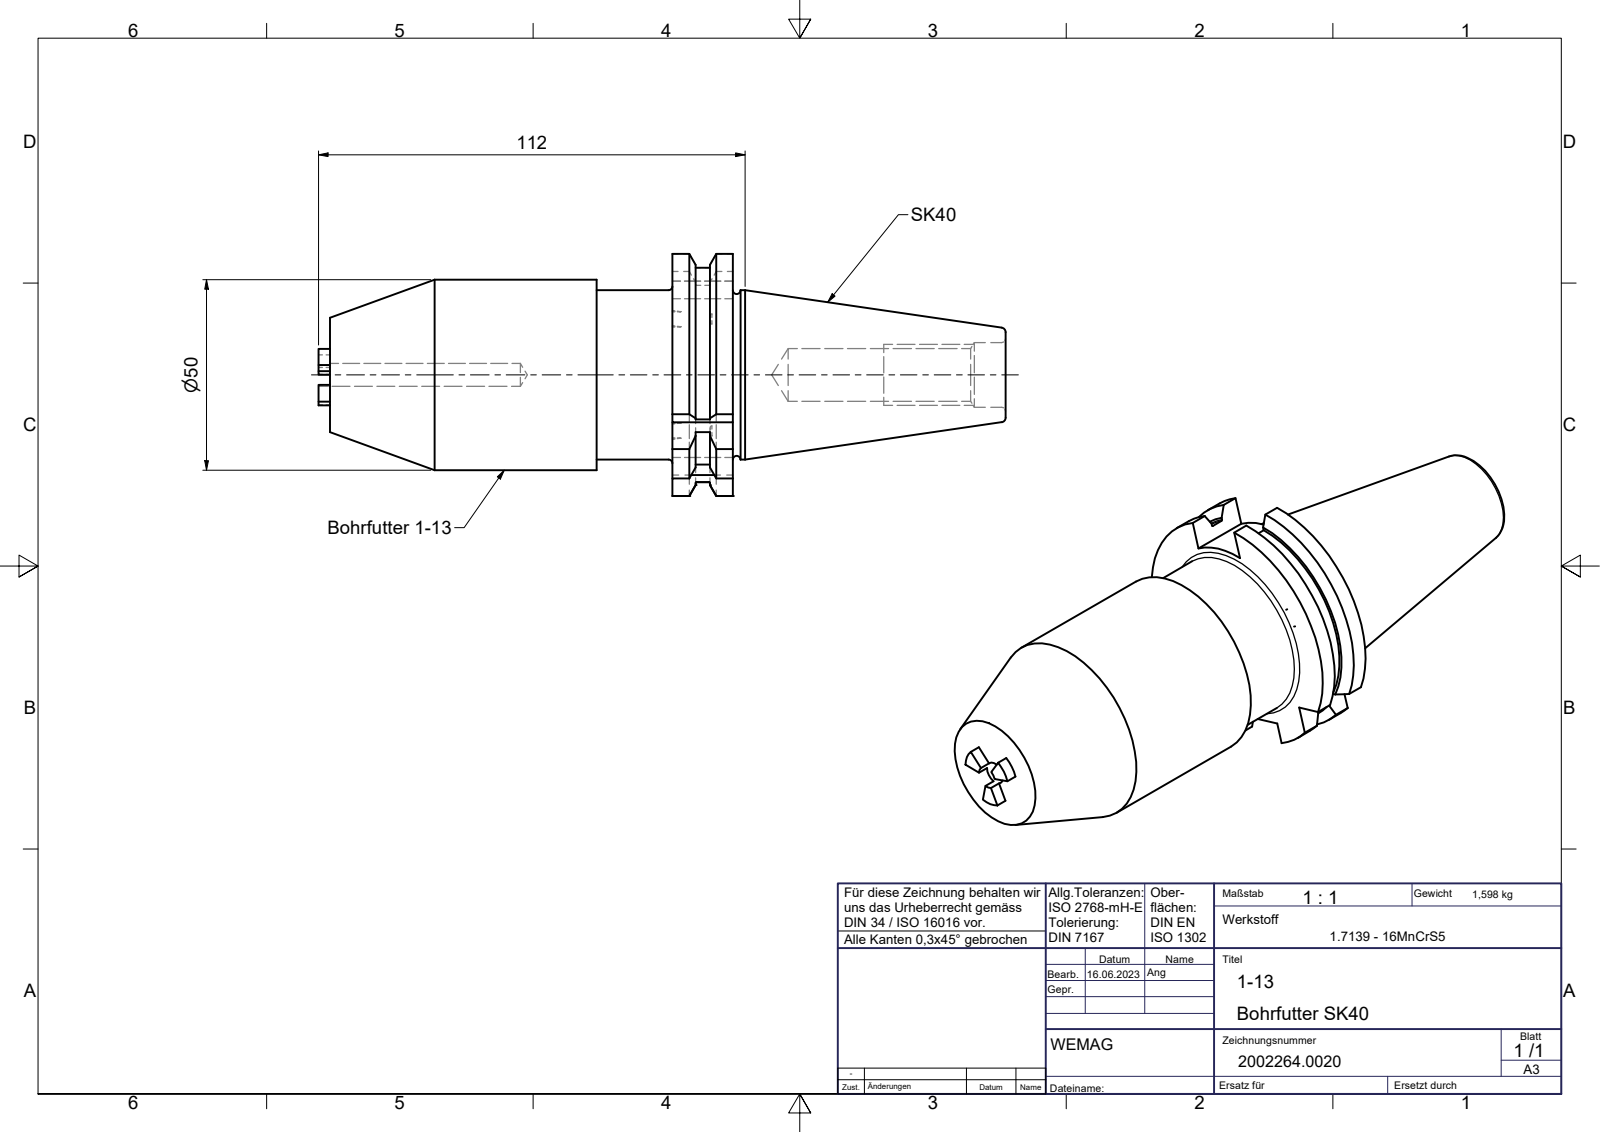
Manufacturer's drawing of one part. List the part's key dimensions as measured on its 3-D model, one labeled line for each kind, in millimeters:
Part name (STEP PRODUCT): 308540113.mb
STEP written by: Autodesk Inventor 2022 (CONFIG_CONTROL_DESIGN)
Units: millimetres
Bodies: 3 solids, 87 faces (35 planar, 31 cylindrical, 21 other)
Overall size (bounding box): 180.4 × 63.55 × 63.55
Volume: 252 987 mm³ · Surface area: 33 274 mm²
Round holes (diameter × count): ⌀6 ×1, ⌀13.84 ×1, ⌀17 ×1
Round bosses / shafts (diameter × count): ⌀50 ×1, ⌀44.45 ×1
Partial cylindrical surfaces — rounded edges, fillets, slot ends (radius × count): R2 ×2, R2.5 ×2, R8 ×1, R24.62 ×1, R28.12 ×1, R31.77 ×1
Main face-to-face distances: 15.9, 89.9, 105.8, 70, 19.9, 35.8, 16.09, 177.4, 107.4, 87.5
